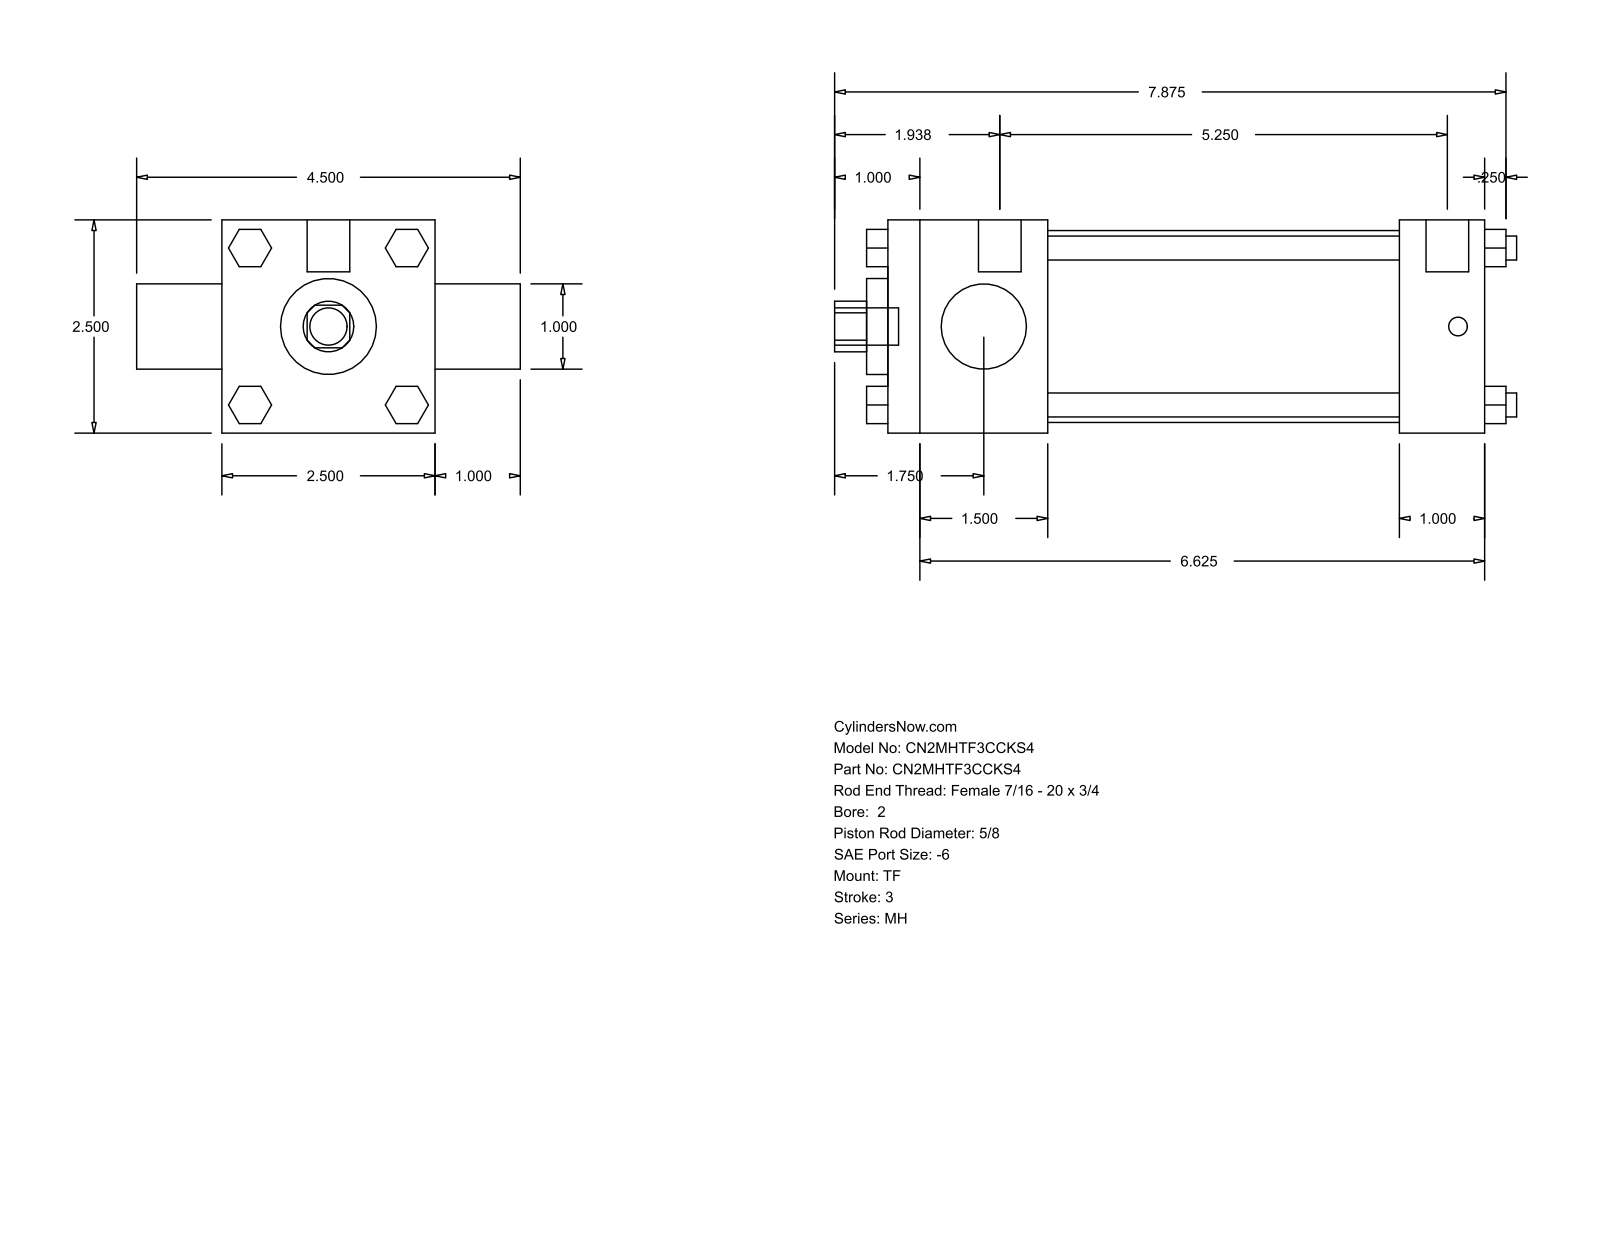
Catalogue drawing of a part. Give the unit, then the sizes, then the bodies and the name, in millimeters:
Units: millimetres
Overall size (bounding box): 203.2 × 114.3 × 63.5
Round holes (diameter × count): ⌀15.88 ×1, ⌀25.4 ×1, ⌀28.57 ×1, ⌀57.15 ×1
Round bosses / shafts (diameter × count): ⌀7.14 ×4, ⌀5.56 ×3, ⌀12.7 ×2, ⌀11.11 ×1
Partial cylindrical surfaces — rounded edges, fillets, slot ends (radius × count): R7.54 ×1
Main face-to-face distances: 63.5, 177.8, 25.4, 47.62, 152.4, 104.78, 130.18, 184.15, 6.35, 88.9
Bodies: 0 solids, 120 faces (92 planar, 28 cylindrical, 0 other)
Part name (STEP PRODUCT): MH_TF__0200_0.625
STEP written by: GSSL Pune (CONFIG_CONTROL_DESIGN)
